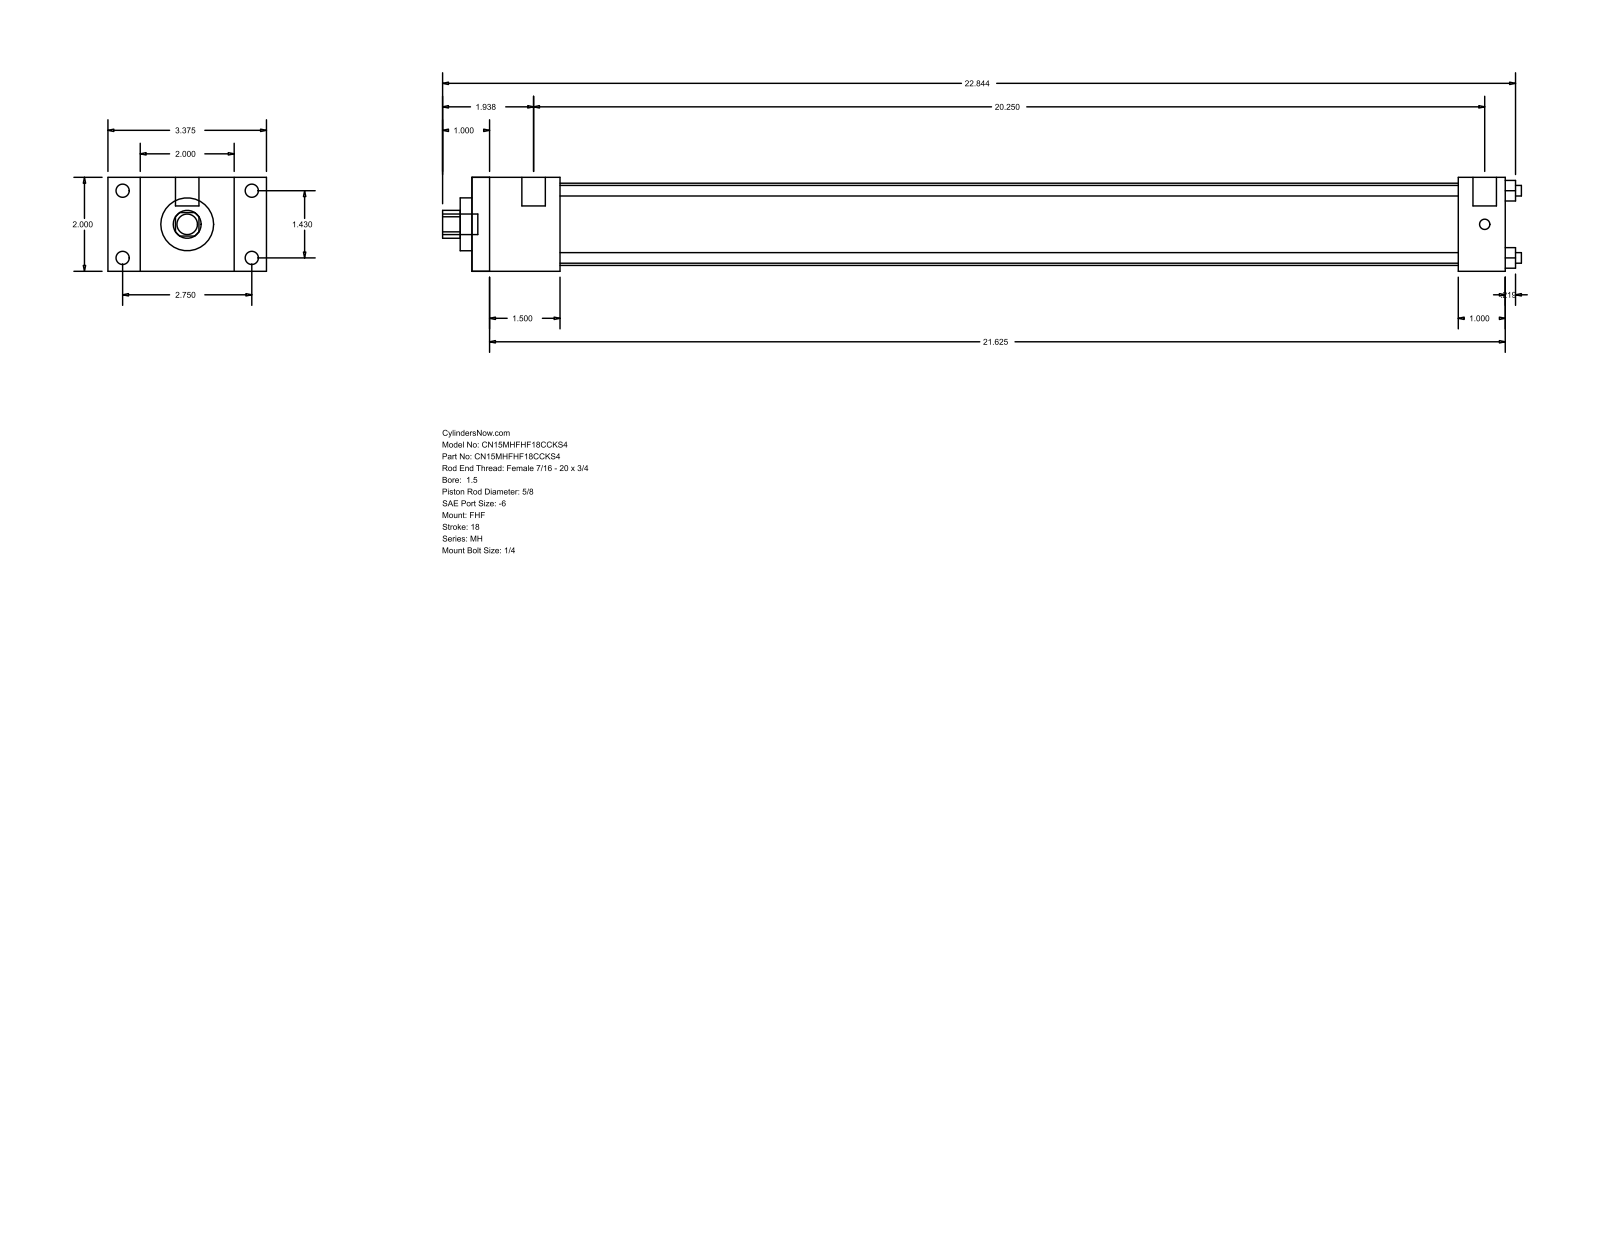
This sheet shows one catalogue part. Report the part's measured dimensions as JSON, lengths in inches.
{"part_name": "MH_FHF__0150_0.625", "step_written_by": "GSSL Pune (CONFIG_CONTROL_DESIGN)", "units": "inches", "bodies": {"solids": 0, "faces": 88, "planar": 60, "cylindrical": 28, "other": 0}, "overall_size": [22.969, 3.375, 2], "round_holes": [[0.225, 4], [0.625, 1], [1.125, 1], [1.75, 1]], "round_bosses_or_shafts": [[0.281, 4], [0.219, 4], [0.5, 2], [0.437, 1]], "partial_cylinders_radius": [[0.297, 1]], "face_to_face_distances": [2, 0.687, 2.687, 1.875, 3.375, 22, 20.125, 21, 19.125, 1], "hole_center_spacings": [1.011, 1.43, 2.022]}
